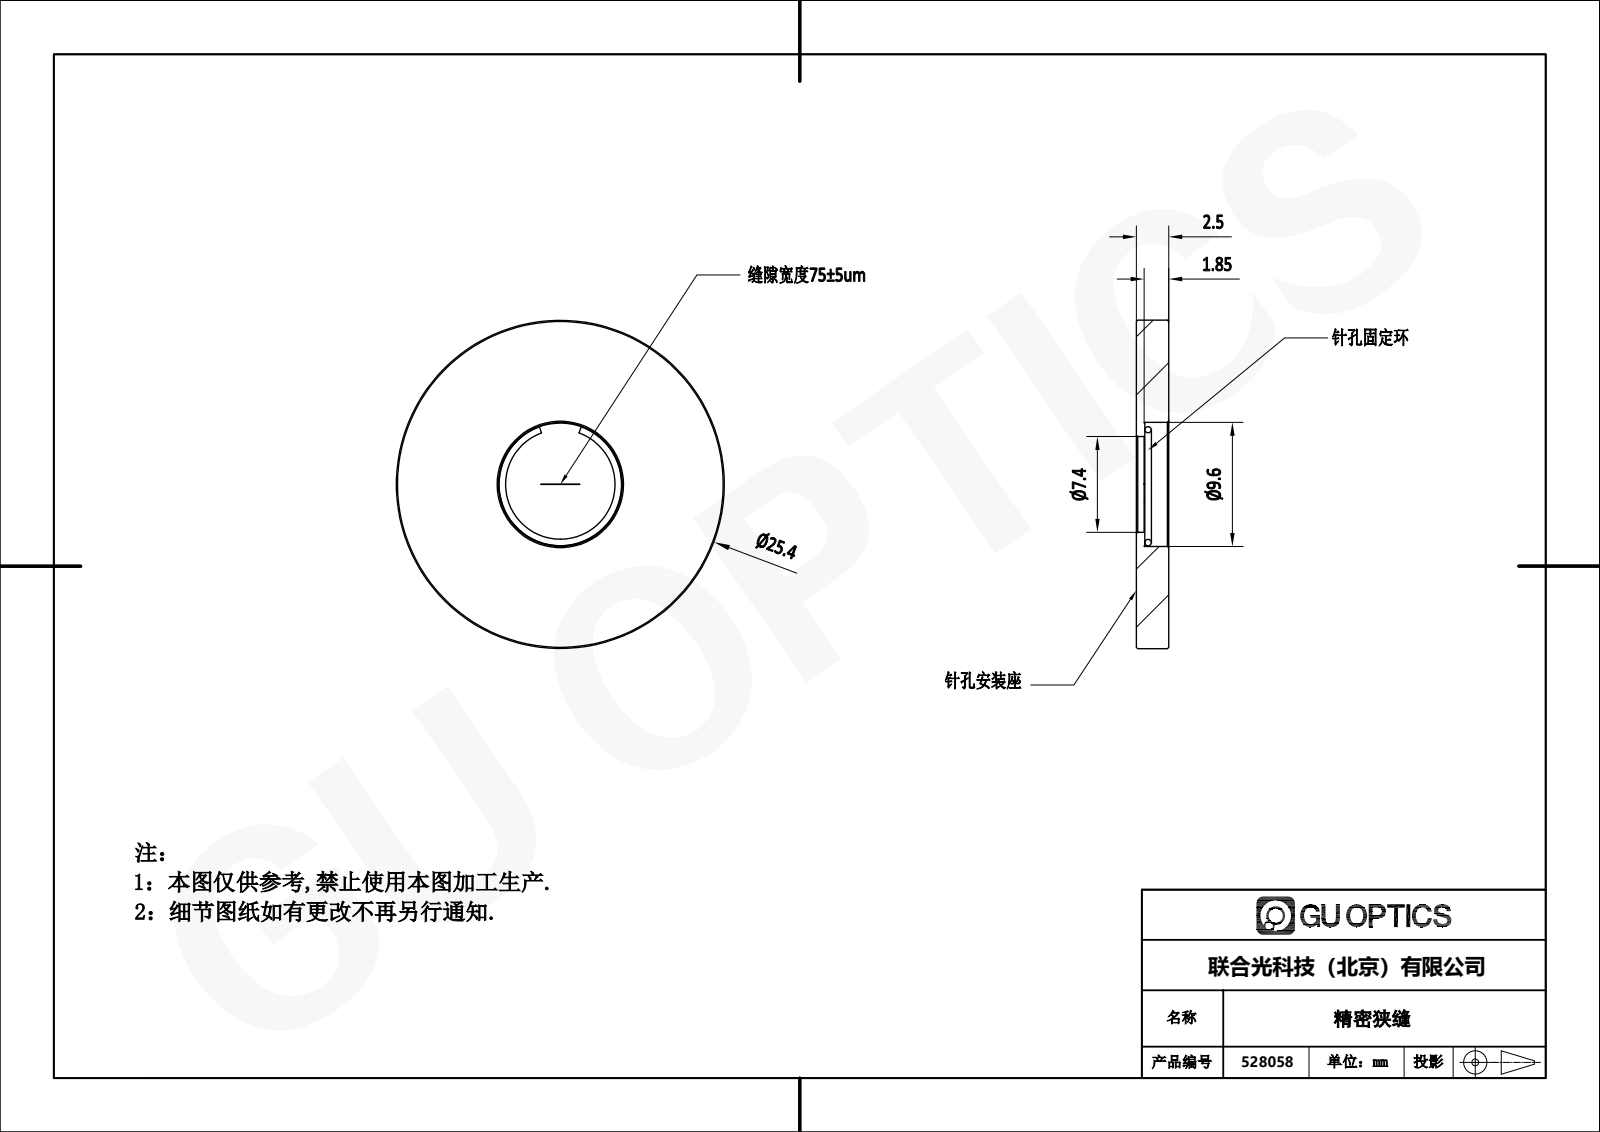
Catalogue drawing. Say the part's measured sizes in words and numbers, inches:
The part is named "528058". Its 3-D file was written by "SolidWorks 2020 (CONFIG_CONTROL_DESIGN)". It is 2 solids with 33 faces: 11 planar, 8 cylindrical and 14 other. Overall it measures 1 by 1 by 0.098 inches. Its volume is 0.068 cubic inches and its surface area 2.035 square inches. Round holes: 1 of diameter 0.291, 1 of diameter 0.378. Round bosses or shafts: 1 of diameter 1, 1 of diameter 0.374. The main face-to-face distances are 0.098, 0.026, 0.073, 0.024, 0.075, 0.118.
